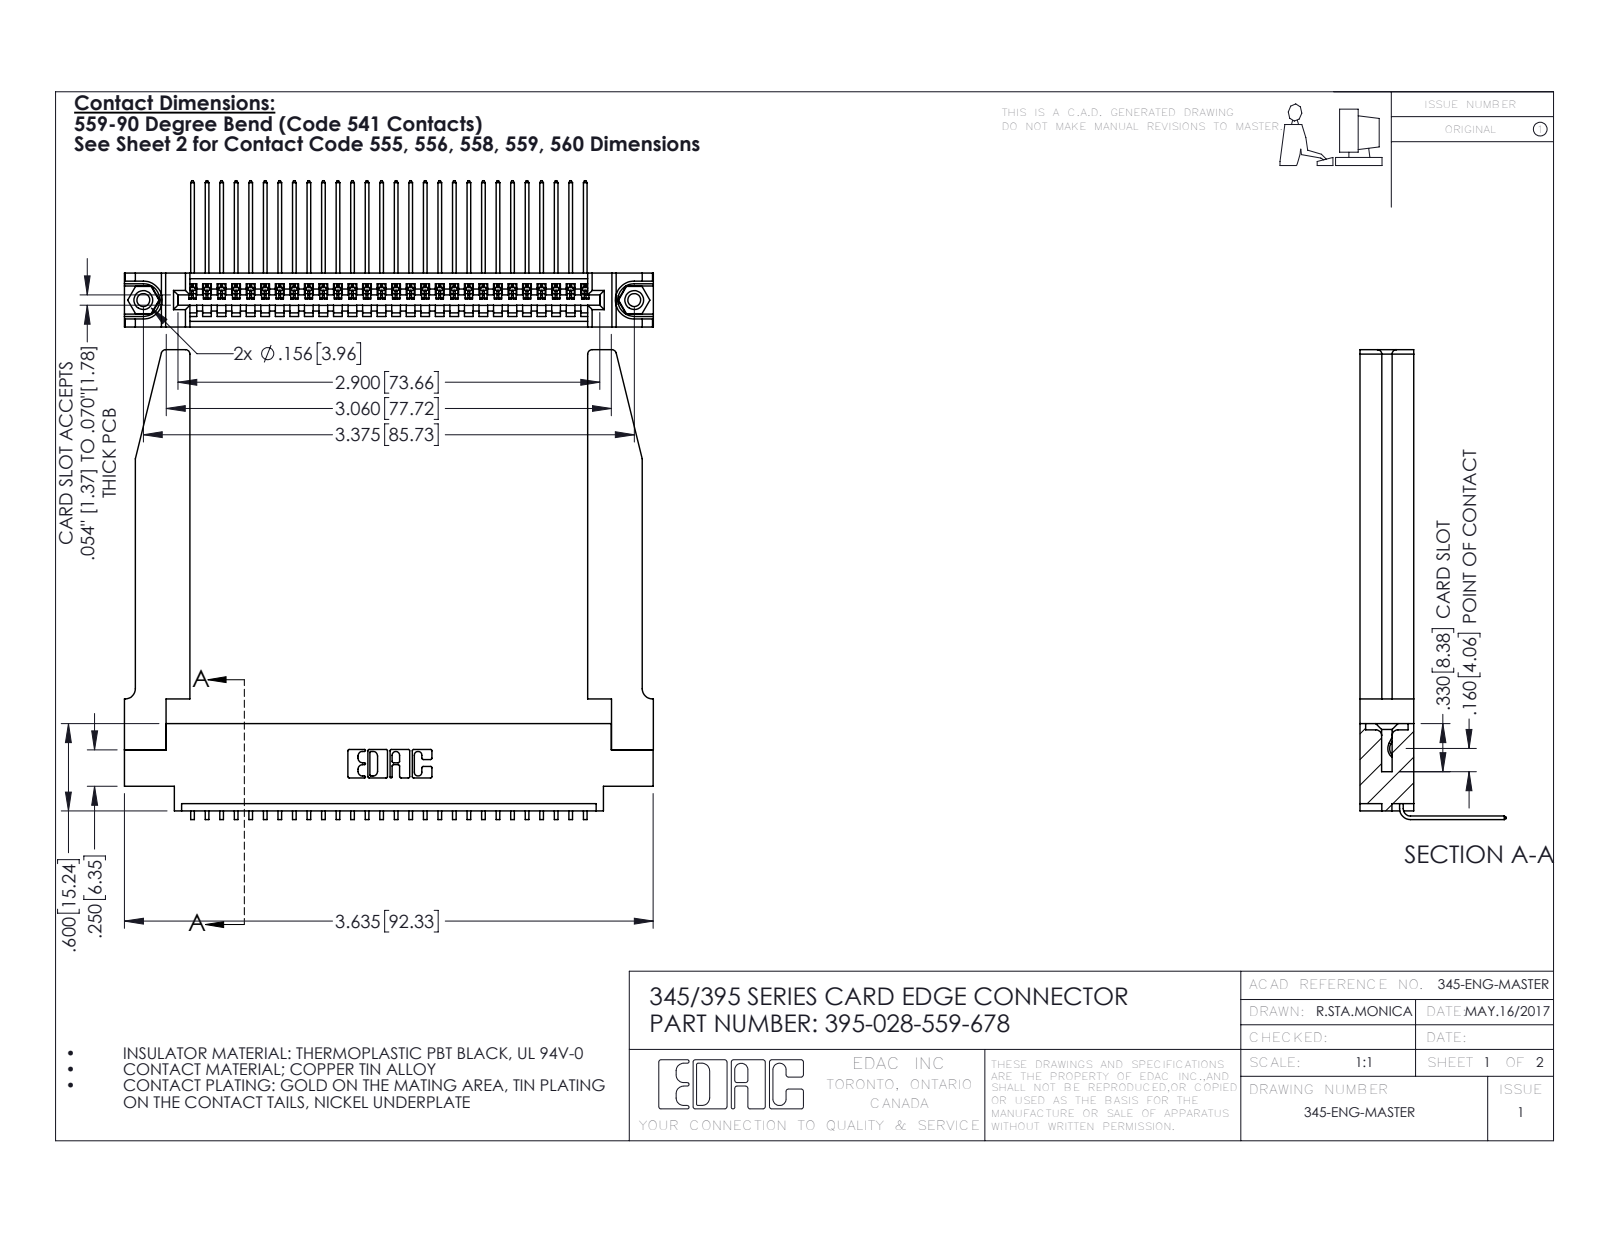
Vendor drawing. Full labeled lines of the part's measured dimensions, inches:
Part name (STEP PRODUCT): 395-028-559-678; 345-220-078_345-220-078; 345-292-001_558 559 Tail - 1; 345 Part_0.170 Offset - 0.156 Dia-TH (+1 more)
STEP written by: SolidWorks 2016 (CONFIG_CONTROL_DESIGN)
Units: inches
Bodies: 33 solids, 2044 faces (1402 planar, 590 cylindrical, 52 other)
Overall size (bounding box): 3.636 × 3.229 × 1.005
Volume: 1.001 in³ · Surface area: 29.15 in²
Round holes (diameter × count): ⌀0.089 ×2, ⌀0.125 ×2, ⌀0.156 ×2, ⌀0.064 ×1
Round bosses / shafts (diameter × count): ⌀0.155 ×2
Partial cylindrical surfaces — rounded edges, fillets, slot ends (radius × count): R0.006 ×56, R0.01 ×22, R0.03 ×8, R0.007 ×6, R0.031 ×6, R0.026 ×3, R0.031 ×2, R0.04 ×2
Main face-to-face distances: 0.37, 0.072, 0.298, 0.098, 0.272, 0.025, 0.2, 0.148, 0.15, 0.225
Hole centre spacings: 0.27, 3.14, 3.375
